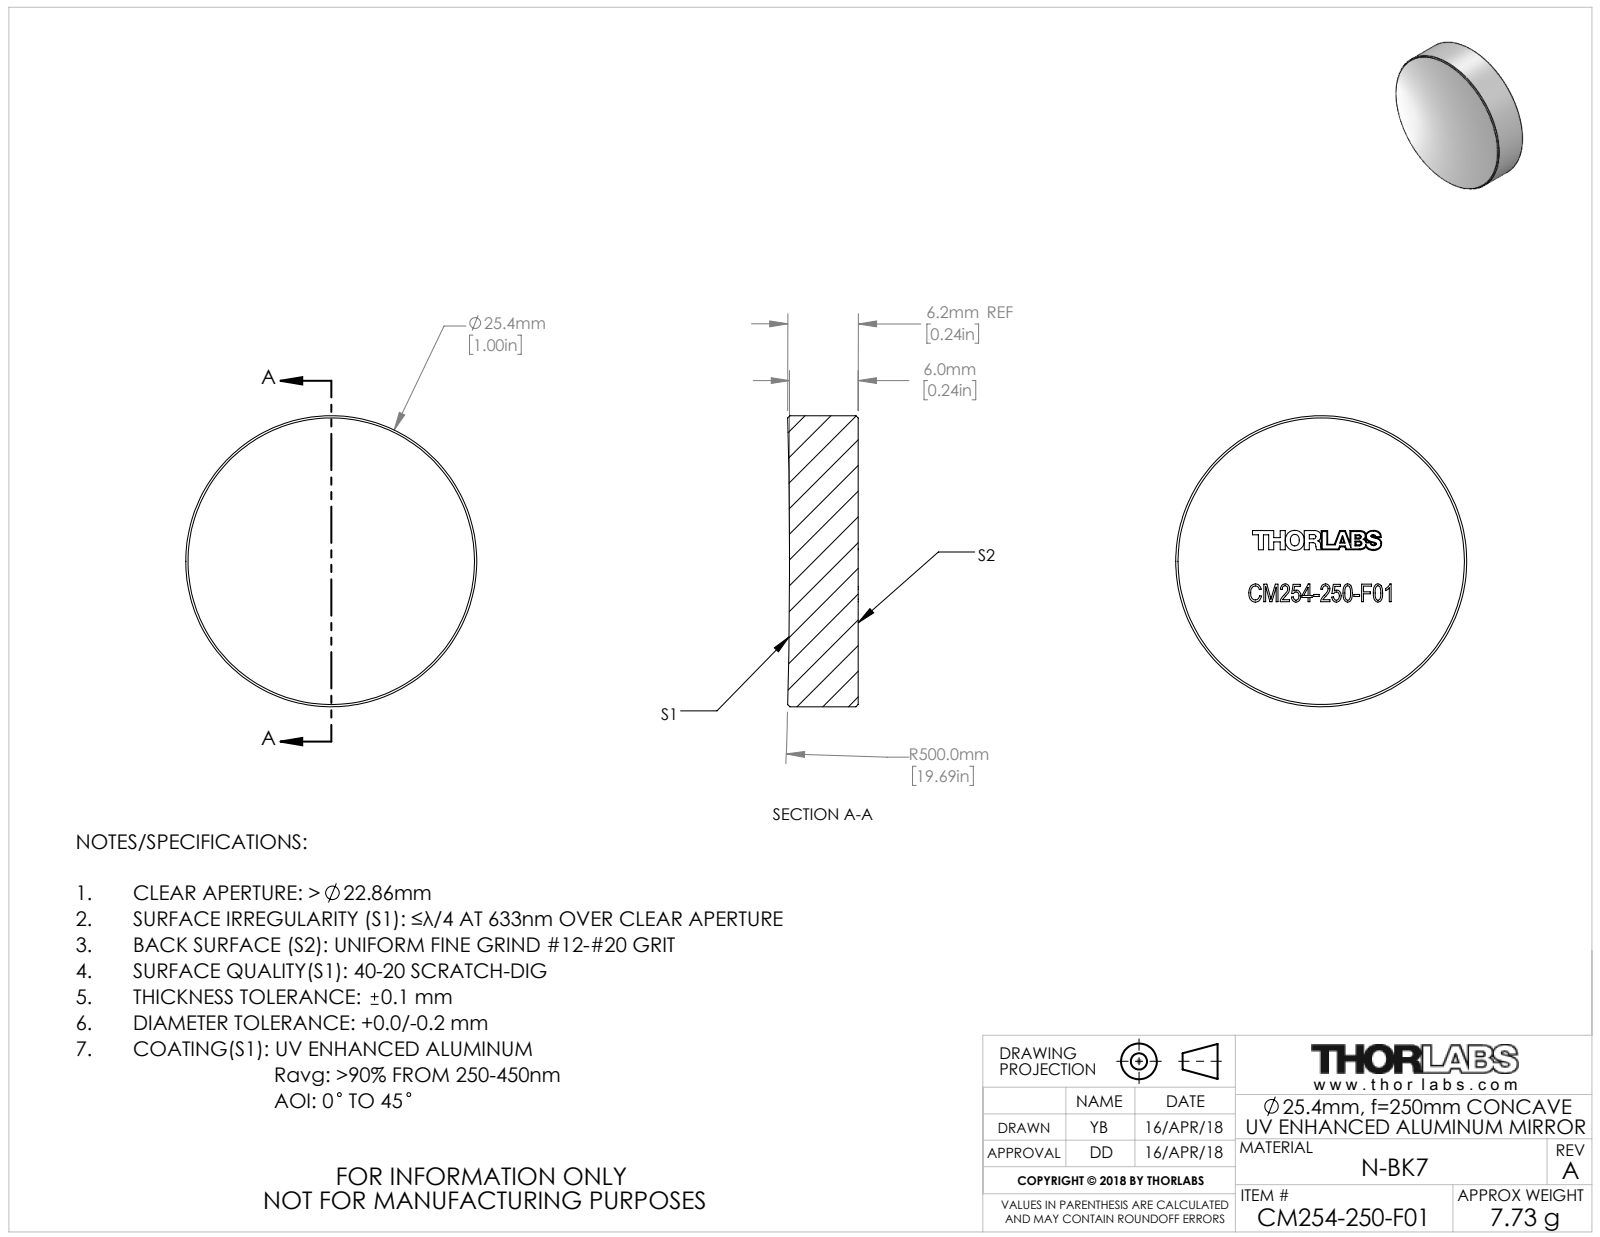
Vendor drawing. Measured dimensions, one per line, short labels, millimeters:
name: TTN153292-E0W
written by: SolidWorks 2018 (CONFIG_CONTROL_DESIGN)
unit: mm
bodies: 1 solid, 40 faces (32 planar, 2 cylindrical, 6 other)
size: 25.4 × 25.4 × 6.16
volume: 3 078 mm³; area: 1 486 mm²
bosses: 1× ⌀25.4
